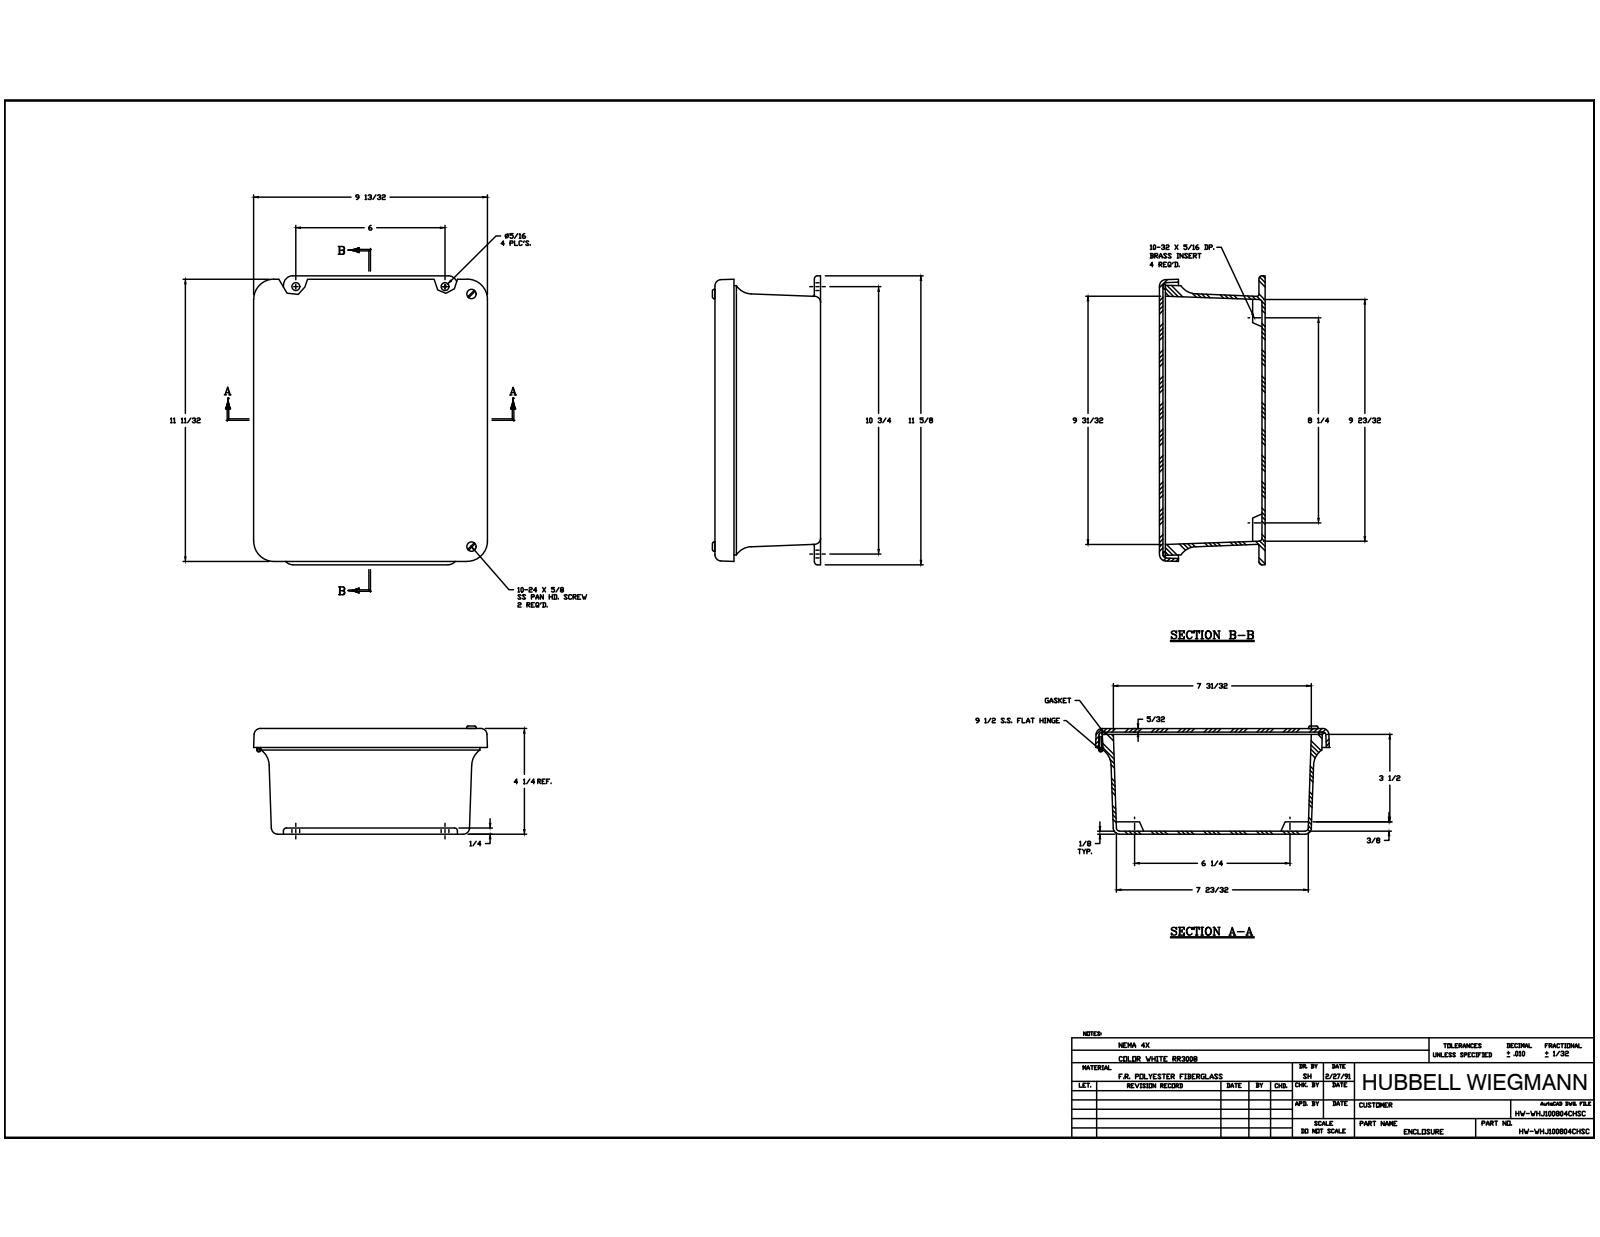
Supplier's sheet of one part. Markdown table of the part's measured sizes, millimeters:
| quantity | value |
| --- | --- |
| part name | J1008HW_2; RMINS45821P_23; RMINS45821P_24; RMINS45821P_25 (+8 more) |
| STEP written by | Autodesk Inventor 2014 (AUTOMOTIVE_DESIGN) |
| units | millimeters |
| bodies | 22 solids, 751 faces (259 planar, 287 cylindrical, 205 other) |
| overall size | 295.27 × 239.61 × 110.86 |
| volume | 992 897 mm³ |
| surface area | 519 748 mm² |
| round holes (diameter × count) | 3.33 × 8, 3.56 × 8, 3.86 × 5, 3.96 × 4, 5.54 × 4, 3.68 × 2, 2.16 × 1, 2.16 × 1 |
| round bosses / shafts (diameter × count) | 6.35 × 8, 3.17 × 8, 6.86 × 6, 4.83 × 2, 3.97 × 2, 3.94 × 1 |
| partial cylindrical surfaces (radius × count) | 0.79 × 20, 3.17 × 12, 6.35 × 8, 5.08 × 5, 9.53 × 4, 19.05 × 4, 1.6 × 2 |
| main face-to-face distances | 3.6, 103.93, 107.53, 3.17, 100.76, 104.36, 3.05, 98.81, 101.98, 1.95 |
| hole center spacings | 152.4, 76.2, 6.35, 33.96, 63.5, 69.85, 184.17, 234.96 |
